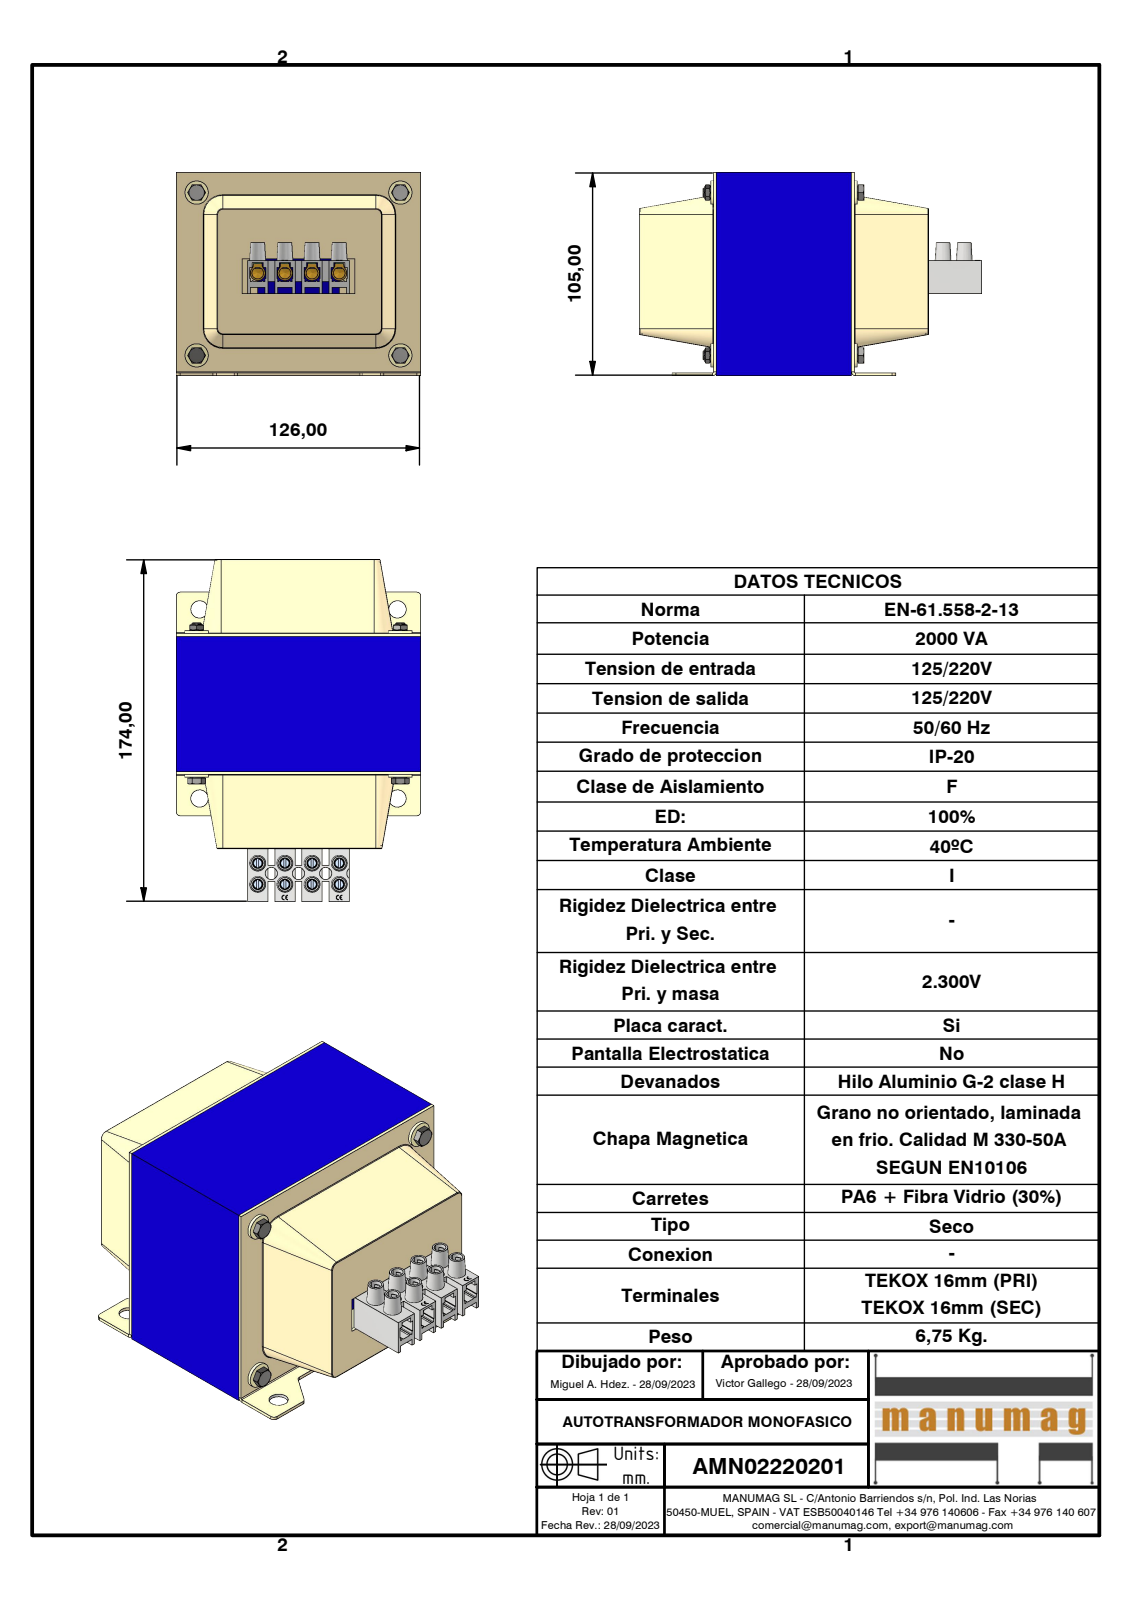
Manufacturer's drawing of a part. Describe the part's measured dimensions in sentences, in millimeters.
The part is named "AMN02220201; EI126 x 105 - 70 Azul; TAPA RC42 CIEGA; TAPA RC42 VENTANA 4 ELEMENTOS 16 (+8 more)". Its 3-D file was written by "Autodesk Inventor 2023 (AUTOMOTIVE_DESIGN)". It is 40 solids with 1657 faces: 1104 planar, 226 cylindrical and 327 other. Overall it measures 177.5 by 126 by 105 millimeters. Its volume is 795 193 cubic millimeters and its surface area 212 206 square millimeters. Round holes: 12 of diameter 3.24, 8 of diameter 5.5, 8 of diameter 6, 4 of diameter 5, 4 of diameter 6.5, 4 of diameter 9, 3 of diameter 6.3. Round bosses or shafts: 8 of diameter 4, 4 of diameter 12, 4 of diameter 6.7, 4 of diameter 5.9, 4 of diameter 4.57. Partial cylindrical surfaces (rounded edges, fillets, slot ends): 16 of radius 0.38, 16 of radius 2.75, 14 of radius 2, 8 of radius 0.82, 8 of radius 3, 6 of radius 0.22, 4 of radius 0.1, 4 of radius 0.81. The main face-to-face distances are 1.5, 21, 38.5, 110, 84, 105, 70, 42, 89.86, 63. The hole center spacings are 14, 28, 8.8, 9, 17.8, 11, 21.67, 21.75.
